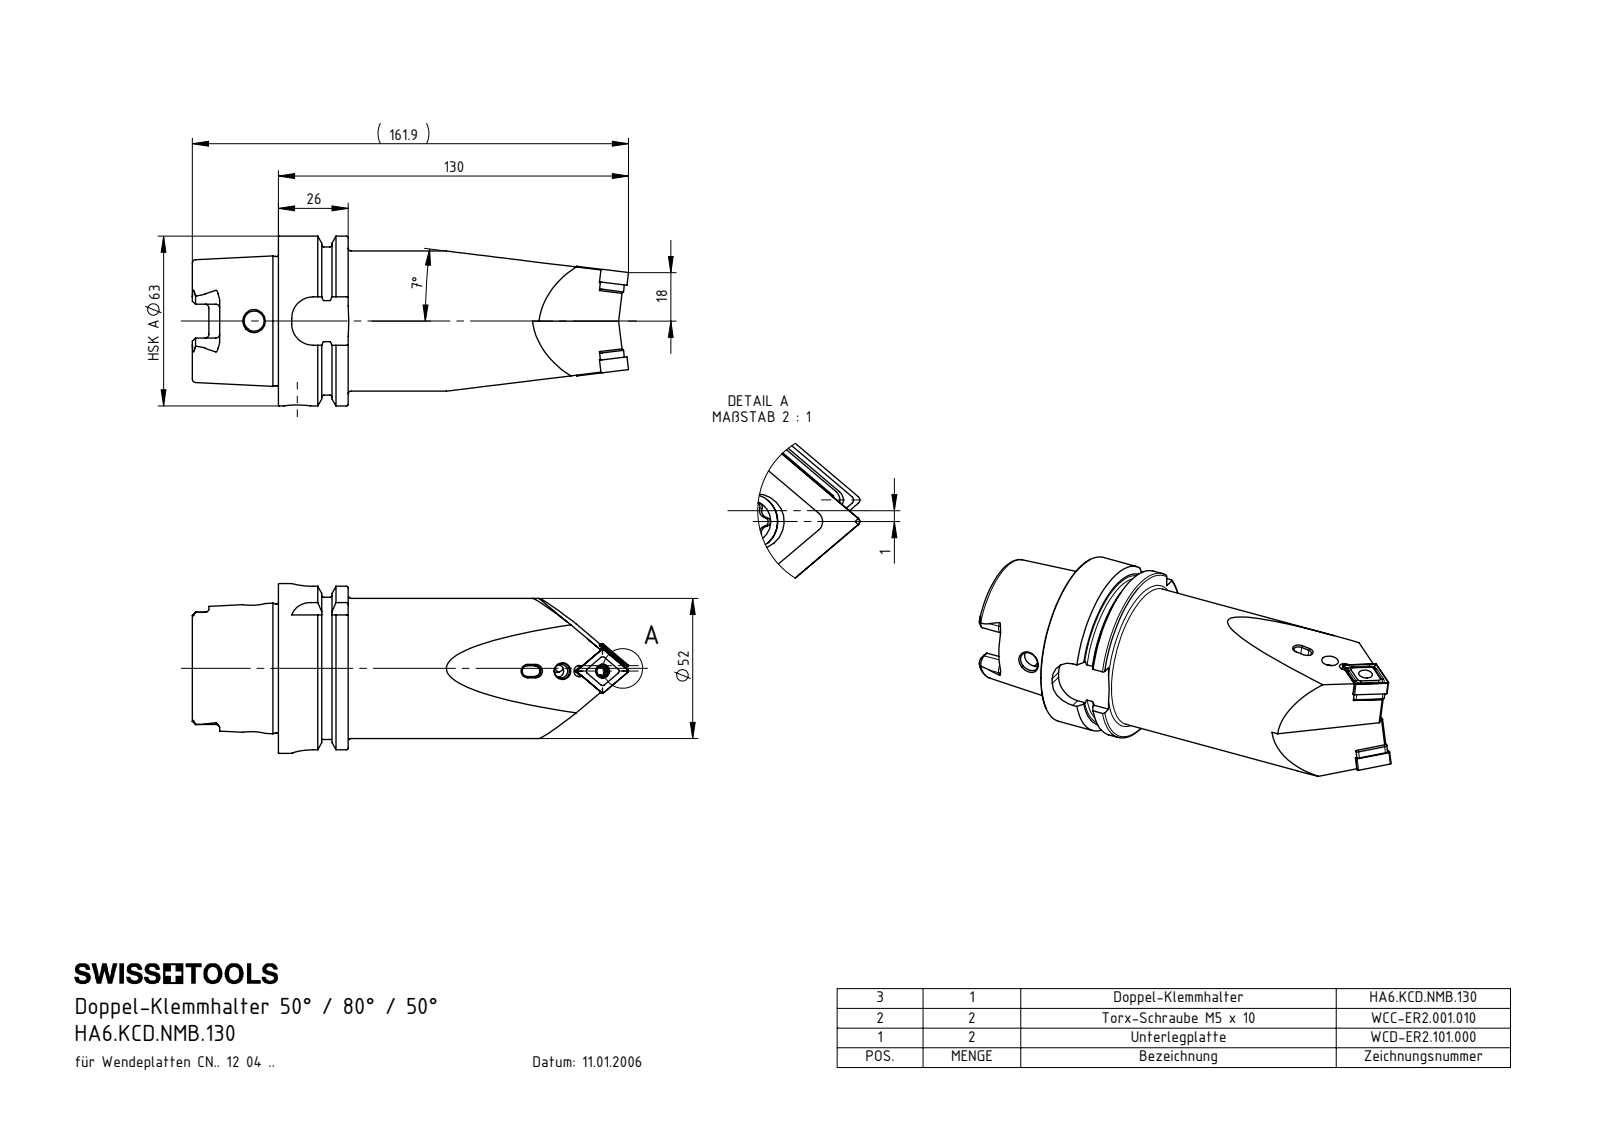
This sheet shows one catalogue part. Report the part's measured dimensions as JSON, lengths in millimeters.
{"part_name": "HA6-KCD.NMB.130_B; CNMG120404; WCC-ER5.102.012_B; WCC-ER3.102.024_C (+5 more)", "step_written_by": "SolidWorks 2017 (AUTOMOTIVE_DESIGN)", "units": "millimeters", "bodies": {"solids": 15, "faces": 500, "planar": 192, "cylindrical": 151, "other": 157}, "overall_size": [161.9, 78.62, 63], "volume_mm3": 263440, "surface_area_mm2": 48849, "round_holes": [[2, 6], [4.2, 4], [7, 4], [3, 2], [5, 2], [5.16, 2], [6.2, 2], [6.4, 2], [8.5, 2], [7.5, 1], [8.4, 1], [10, 1]], "round_bosses_or_shafts": [[14, 2], [11.5, 2], [7, 2], [6.8, 2], [6.2, 2], [6, 2], [5, 2], [4, 2]], "partial_cylinders_radius": [[0.39, 12], [0.4, 8], [1, 8], [0.69, 6], [0.69, 6], [1.4, 6], [1.5, 6], [2, 4]], "face_to_face_distances": [25.95, 16, 9.95, 11.85, 4.47, 8.94, 5.76, 1.29, 3.18, 7.65], "hole_center_spacings": [6.17, 6.36, 6.37, 8, 8.01, 8.2, 8.57, 8.63]}
